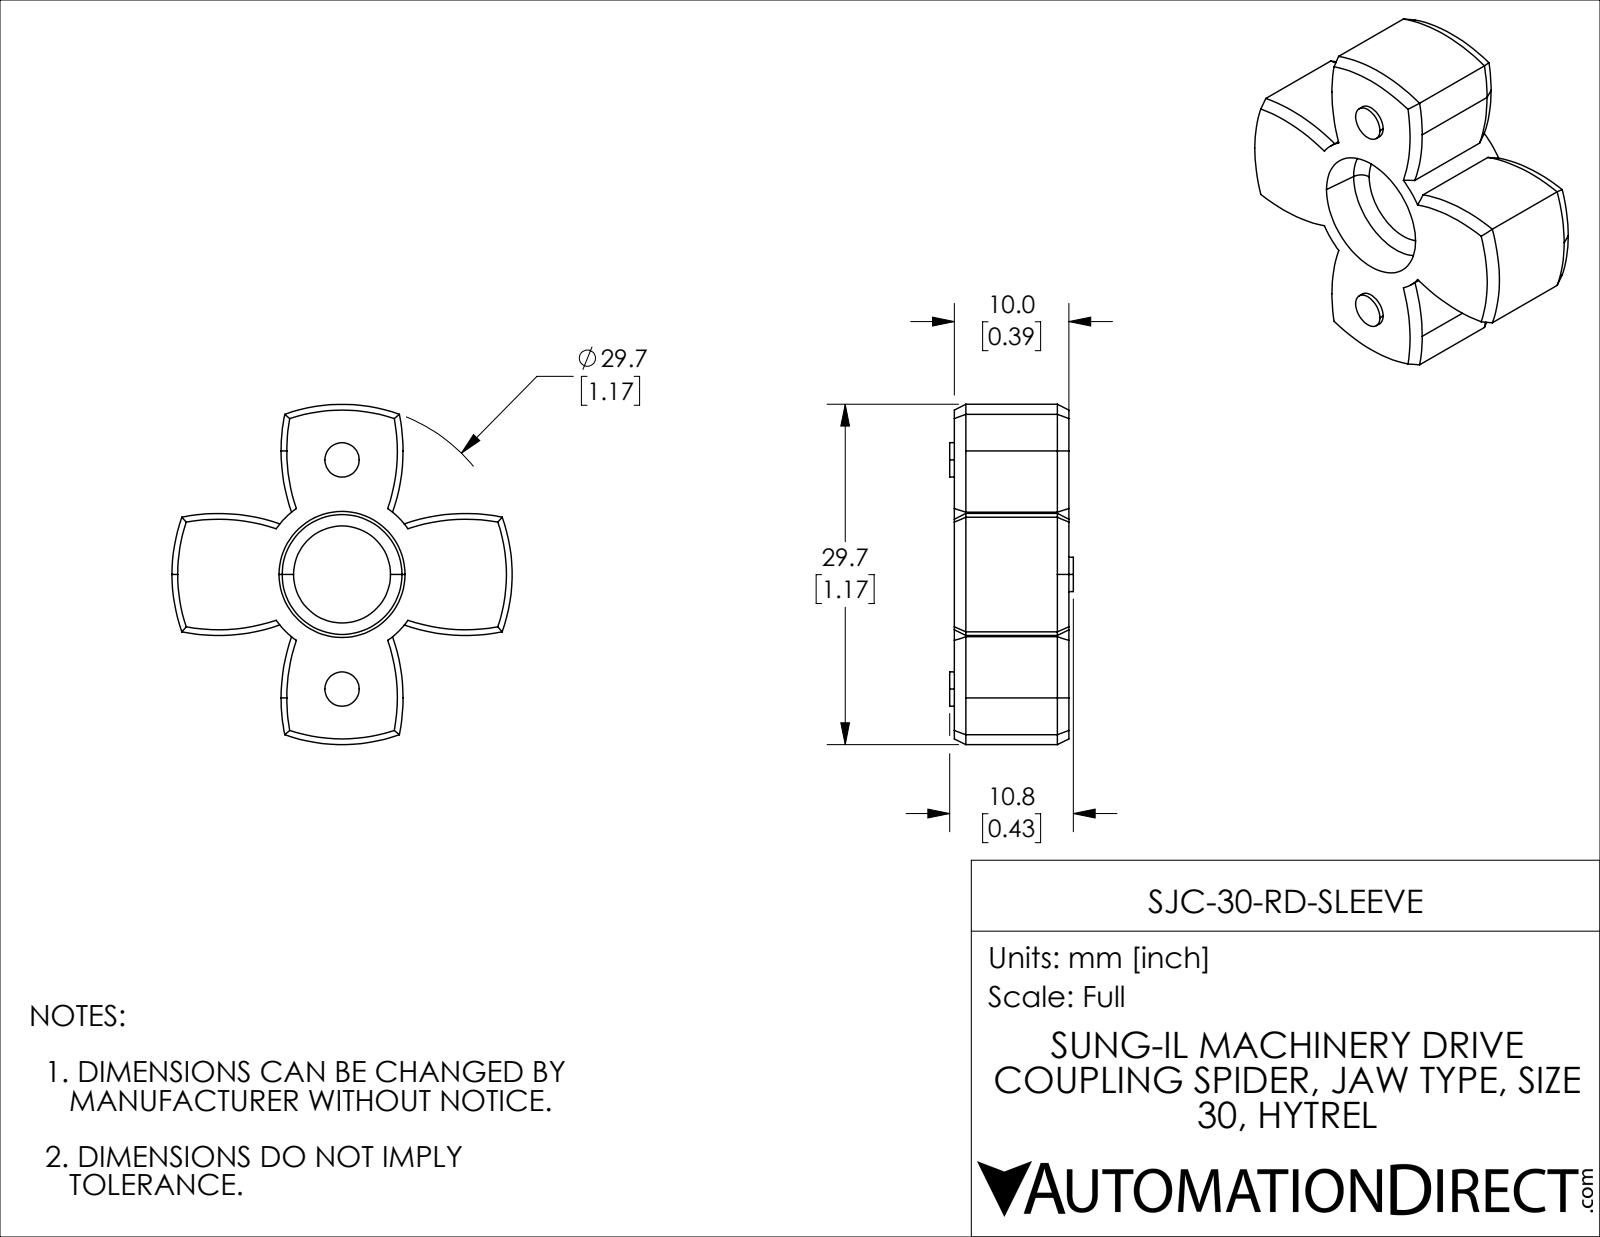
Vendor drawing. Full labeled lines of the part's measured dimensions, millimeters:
Part name (STEP PRODUCT): SJC-30-RD-SLEEVE
STEP written by: SolidWorks 2021 (CONFIG_CONTROL_DESIGN)
Units: millimetres
Bodies: 1 solid, 73 faces (8 planar, 27 cylindrical, 38 other)
Overall size (bounding box): 29.7 × 29.7 × 10.8
Volume: 4 135 mm³ · Surface area: 2 287 mm²
Round bosses / shafts (diameter × count): ⌀3 ×4
Partial cylindrical surfaces — rounded edges, fillets, slot ends (radius × count): R16.1 ×4, R7 ×1, R14.85 ×1
Main face-to-face distances: 10, 4, 6, 2, 0.4, 4.4, 6.4, 10.4, 10.8
